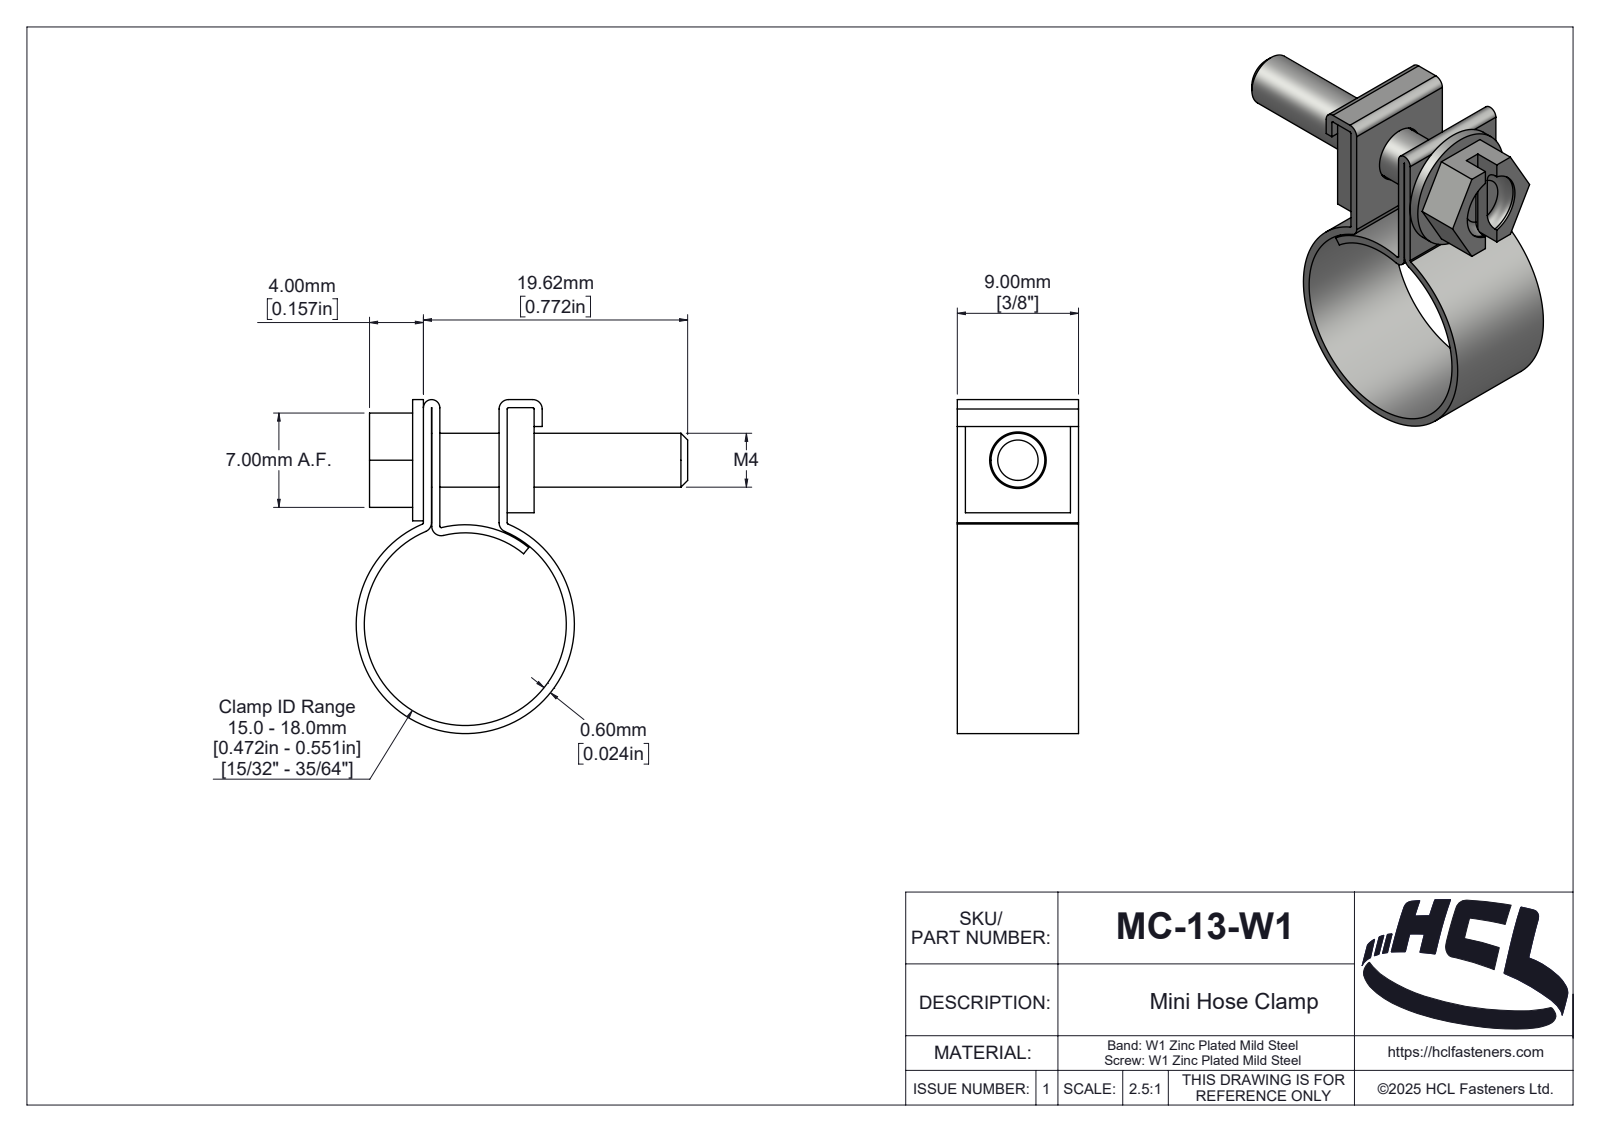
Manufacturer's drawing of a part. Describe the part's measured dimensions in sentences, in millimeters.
The part is named "MC-13-W1". Its 3-D file was written by "SolidWorks 2025 (AUTOMOTIVE_DESIGN)". It is 3 solids with 175 faces: 38 planar, 84 cylindrical and 53 other. Overall it measures 24.79 by 24.61 by 9 millimeters. Its volume is 915 cubic millimeters and its surface area 2 207 square millimeters. Round holes: 1 of diameter 4.2, 1 of diameter 5, 1 of diameter 15. Round bosses or shafts: 1 of diameter 16.2, 1 of diameter 9, 1 of diameter 4. Partial cylindrical surfaces (rounded edges, fillets, slot ends): 5 of radius 0.1, 5 of radius 0.7, 1 of radius 0.2, 1 of radius 0.61, 1 of radius 0.81, 1 of radius 1.01, 1 of radius 1.06, 1 of radius 1.28. The main face-to-face distances are 0.6, 0.62, 5, 5.62, 6.22, 7, 2, 2.6, 8.22, 7.6.
